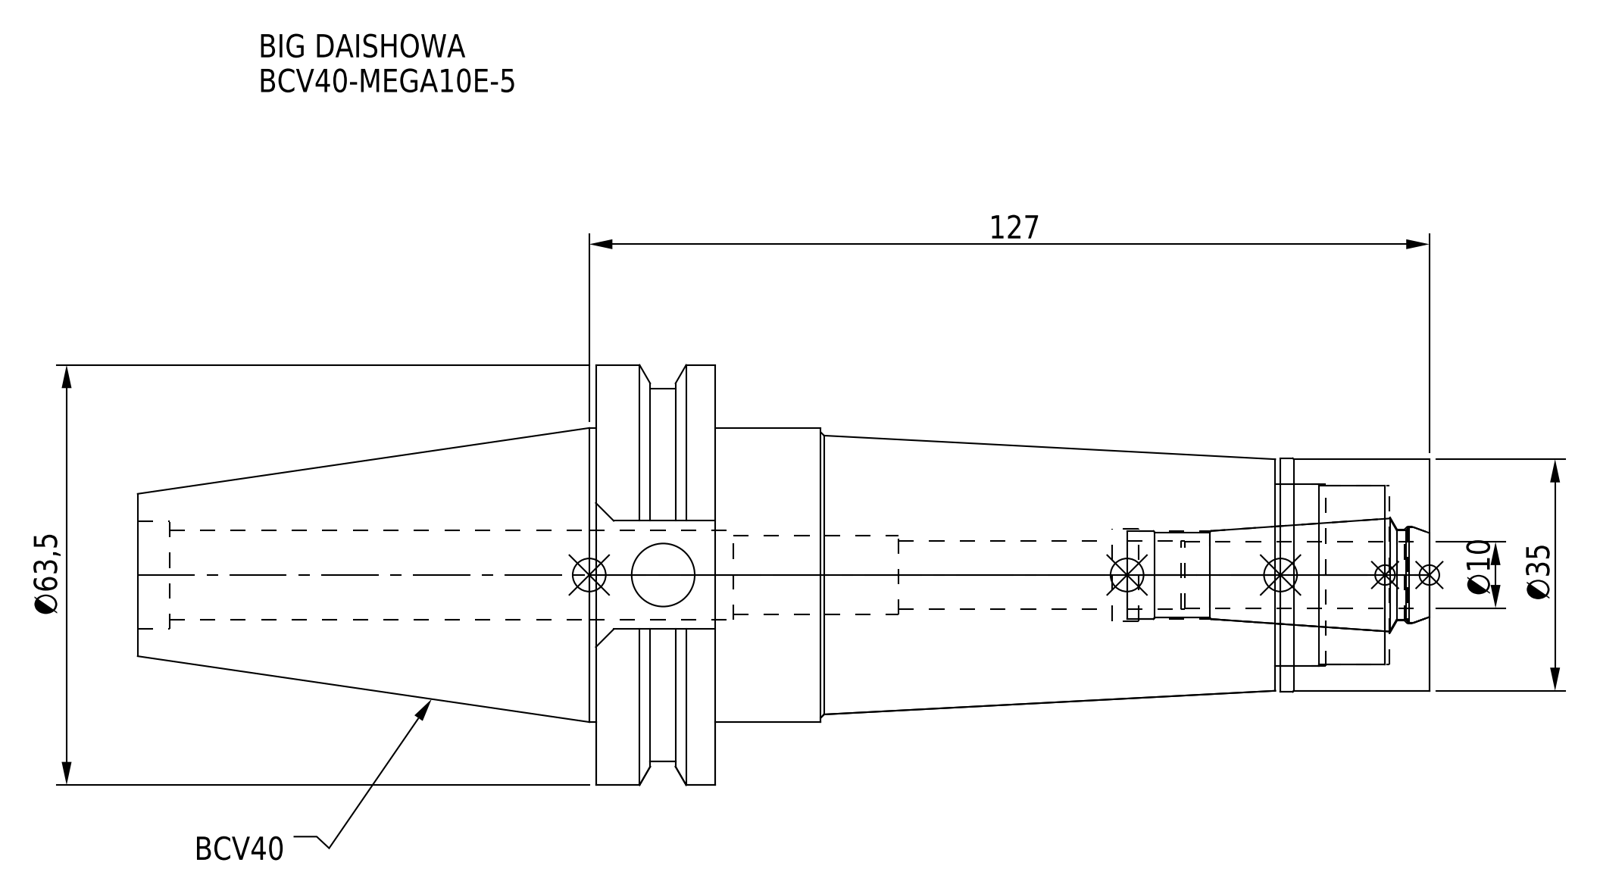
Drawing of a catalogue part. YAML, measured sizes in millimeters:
part_name: "BCV40ME10050-010_ASM.stp; BCV40-MEGA10E-5_1.stp; BCV40-MEGA10E-5; MEN10_1.stp (+3 more)"
step_written_by: "SolidWorks 2019 (CONFIG_CONTROL_DESIGN)"
units: millimeters
bodies: {solids: 2, faces: 93, planar: 31, cylindrical: 42, other: 20}
overall_size: [195.25, 63.5, 61.35]
volume: 217123
surface_area: 41834
round_holes:
  - {diameter: 9.53, count: 1}
  - {diameter: 10.4, count: 1}
  - {diameter: 12, count: 1}
  - {diameter: 13.3, count: 1}
  - {diameter: 13.6, count: 1}
  - {diameter: 13.8, count: 1}
  - {diameter: 13.9, count: 1}
  - {diameter: 14.7, count: 1}
  - {diameter: 16.32, count: 1}
  - {diameter: 27, count: 1}
  - {diameter: 27.5, count: 1}
round_bosses_or_shafts:
  - {diameter: 63.5, count: 1}
  - {diameter: 56.36, count: 1}
  - {diameter: 44.45, count: 1}
  - {diameter: 35.3, count: 1}
  - {diameter: 35, count: 1}
face_to_face_distances: [18.05, 107.95, 126, 6, 22.5, 85.45, 103.5, 23.3, 0.8, 84.65]
